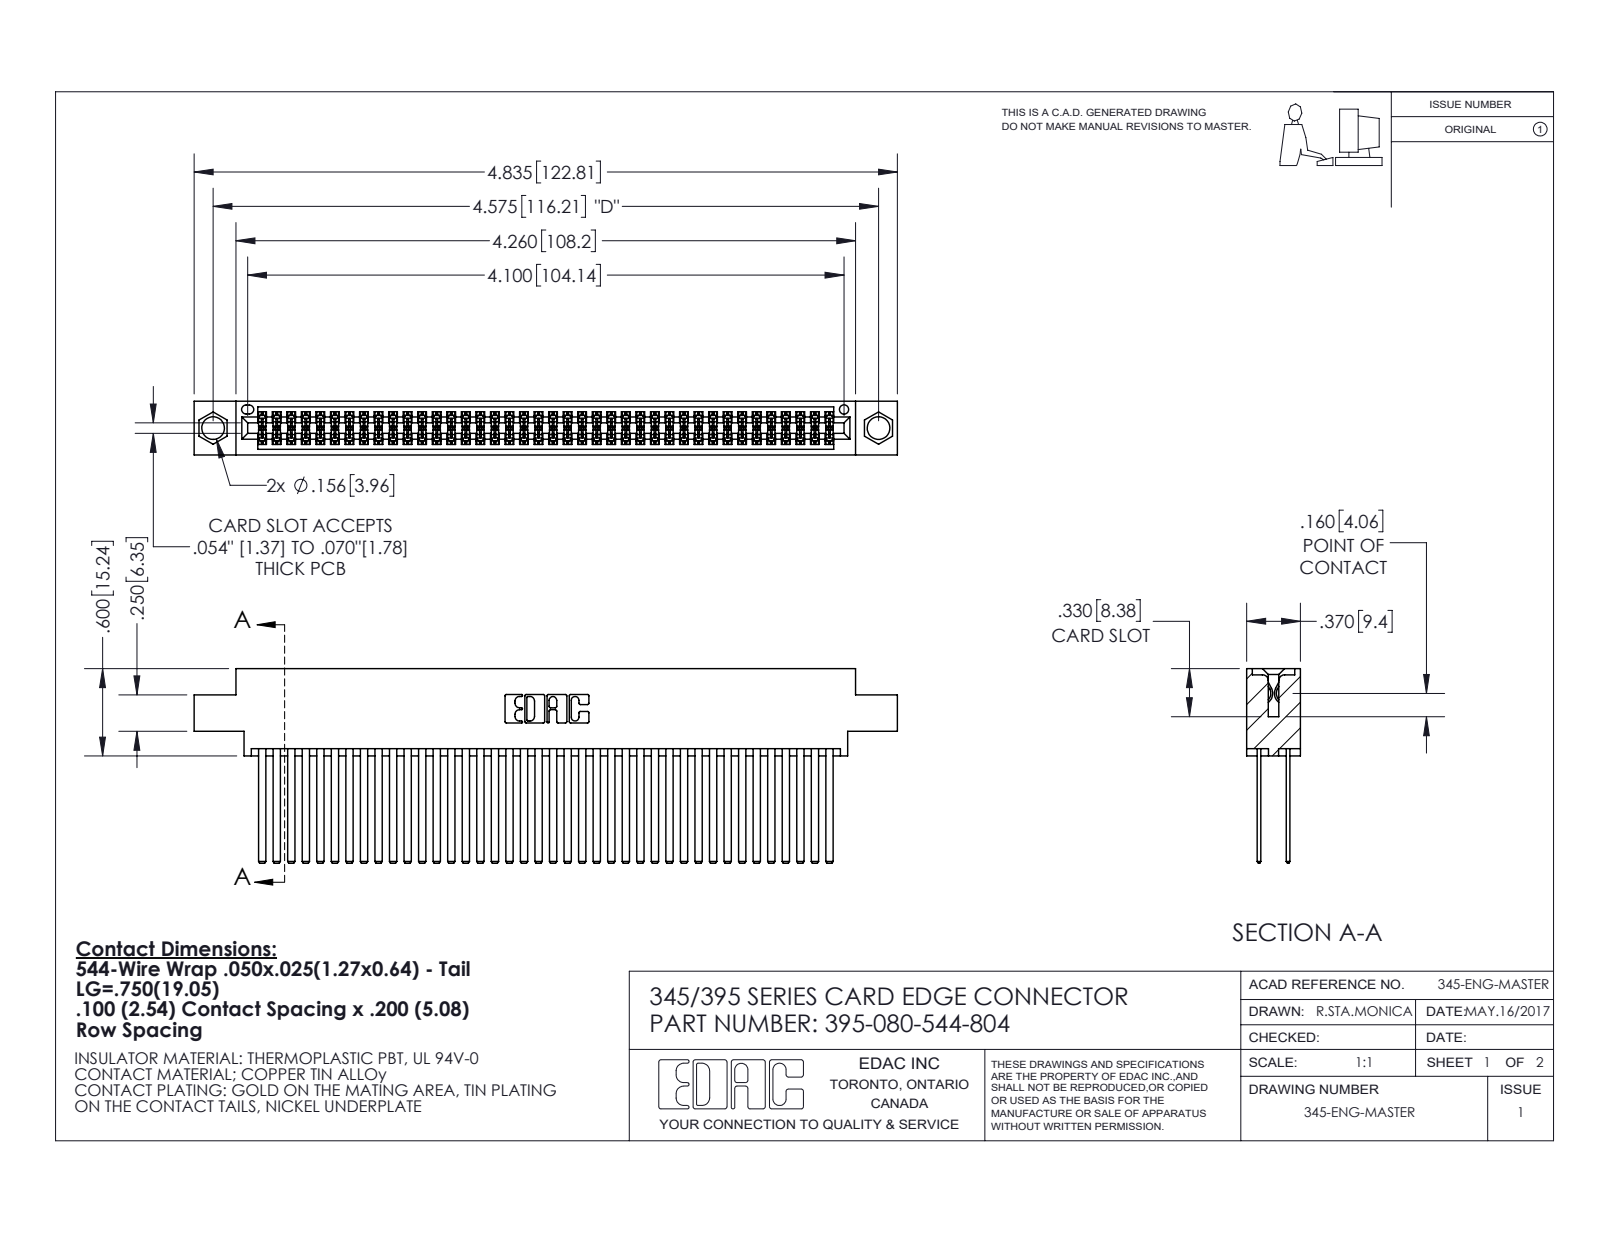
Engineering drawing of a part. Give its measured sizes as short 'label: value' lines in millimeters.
name: 345-292-001_345-293-144; 395-080-544-804; 345 Part_0.170 Offset - 0.156 Dia-TI
written by: SolidWorks 2020 (CONFIG_CONTROL_DESIGN)
unit: mm
bodies: 81 solids, 3664 faces (2418 planar, 1246 cylindrical, 0 other)
size: 122.8 × 34 × 9.4
volume: 12 800 mm³; area: 22 180 mm²
holes: 2× ⌀4, 1× ⌀1.6
rounds: 120× R0.2, 22× R0.3, 6× R0.2, 6× R0.8, 3× R0.7, 2× R0.4, 2× R0.5, 2× R0.6
face distances: 5.1, 0.6, 1.8, 2.5, 6.9, 7.6, 5.7, 4.4, 9.4, 3.8
hole spacings: 6.9, 110.2, 116.2
